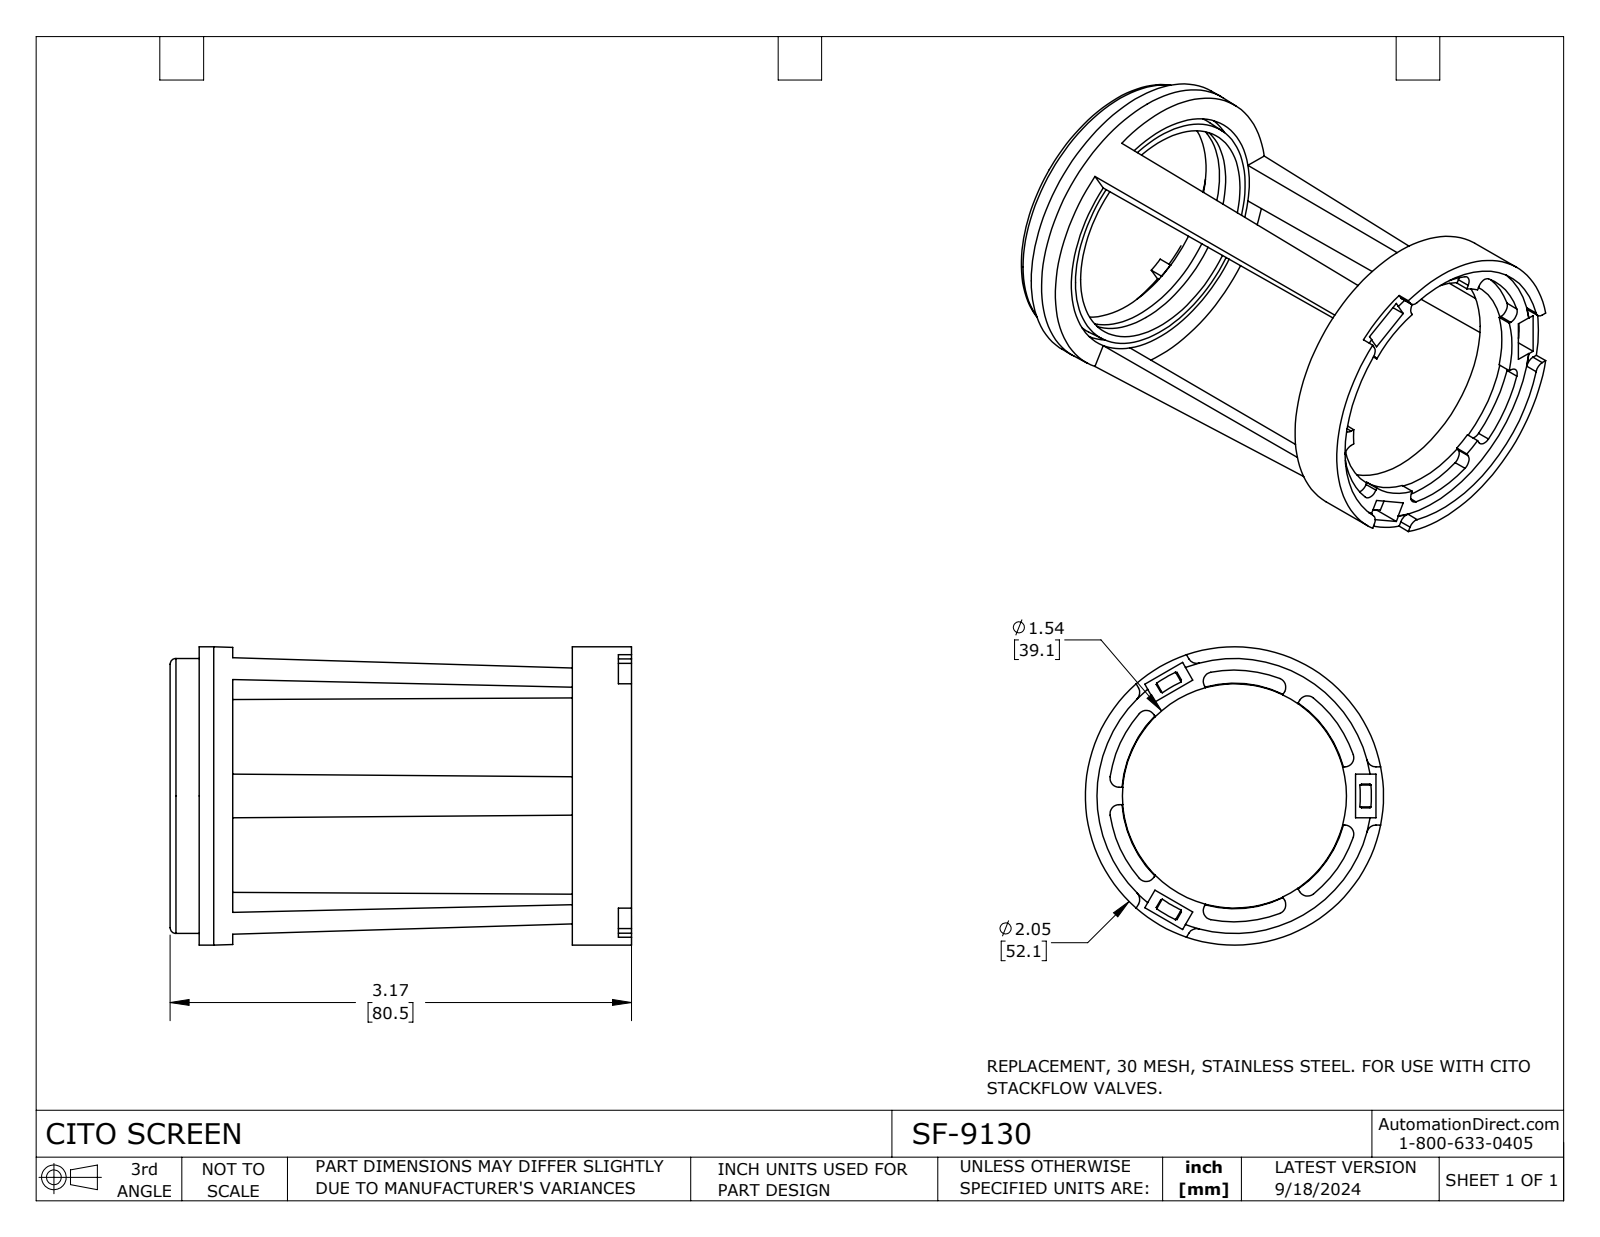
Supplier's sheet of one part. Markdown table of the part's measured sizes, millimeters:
| quantity | value |
| --- | --- |
| part name | SF-9130 |
| STEP written by | SolidWorks 2023 (CONFIG_CONTROL_DESIGN) |
| units | millimeters |
| bodies | 2 solids, 191 faces (112 planar, 65 cylindrical, 14 other) |
| overall size | 80.5 × 52.1 × 52.1 |
| volume | 17 780 mm³ |
| surface area | 15 450 mm² |
| round holes (diameter × count) | 39.4 × 1, 43.9 × 1, 48 × 1 |
| round bosses / shafts (diameter × count) | 52.1 × 1, 41.9 × 1 |
| partial cylindrical surfaces (radius × count) | 1.6 × 10, 1.6 × 8, 19.6 × 1, 19.6 × 1 |
| main face-to-face distances | 59.3, 2.5, 67.3, 8, 5.8, 65.2, 73.1, 75.7, 8.4, 67.7 |
